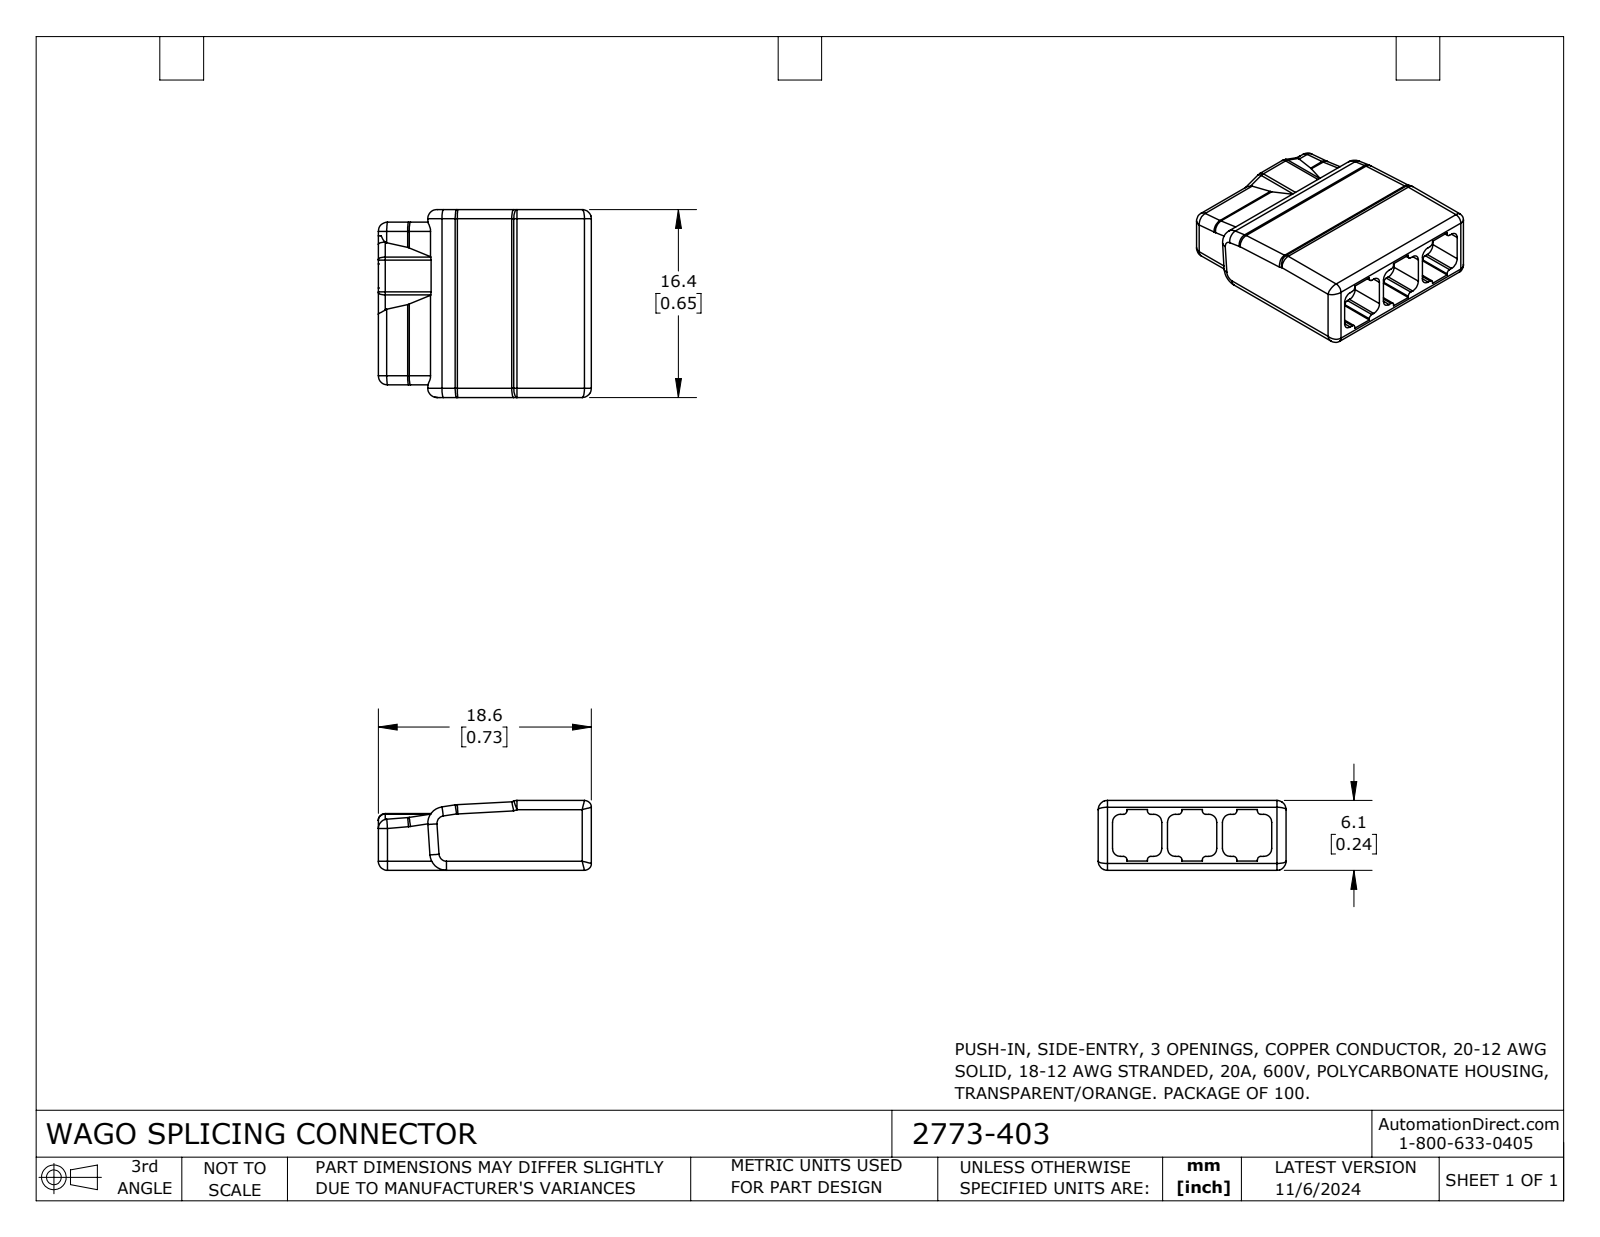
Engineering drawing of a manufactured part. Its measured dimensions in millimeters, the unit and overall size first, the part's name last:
Units: millimetres
Overall size (bounding box): 18.6 × 16.4 × 6.1
Partial cylindrical surfaces — rounded edges, fillets, slot ends (radius × count): R0.8 ×27, R0.3 ×12, R0.7 ×12, R0.6 ×5, R1.45 ×2, R2 ×2
Main face-to-face distances: 6.1, 16.4, 15.6, 4.8, 0.8, 3, 5.3, 1.1, 15.3, 4.3
Volume: 1 480 mm³ · Surface area: 1 090 mm²
Bodies: 1 solid, 150 faces (66 planar, 63 cylindrical, 21 other)
Part name (STEP PRODUCT): 2773-403
STEP written by: SolidWorks 2023 (CONFIG_CONTROL_DESIGN)
